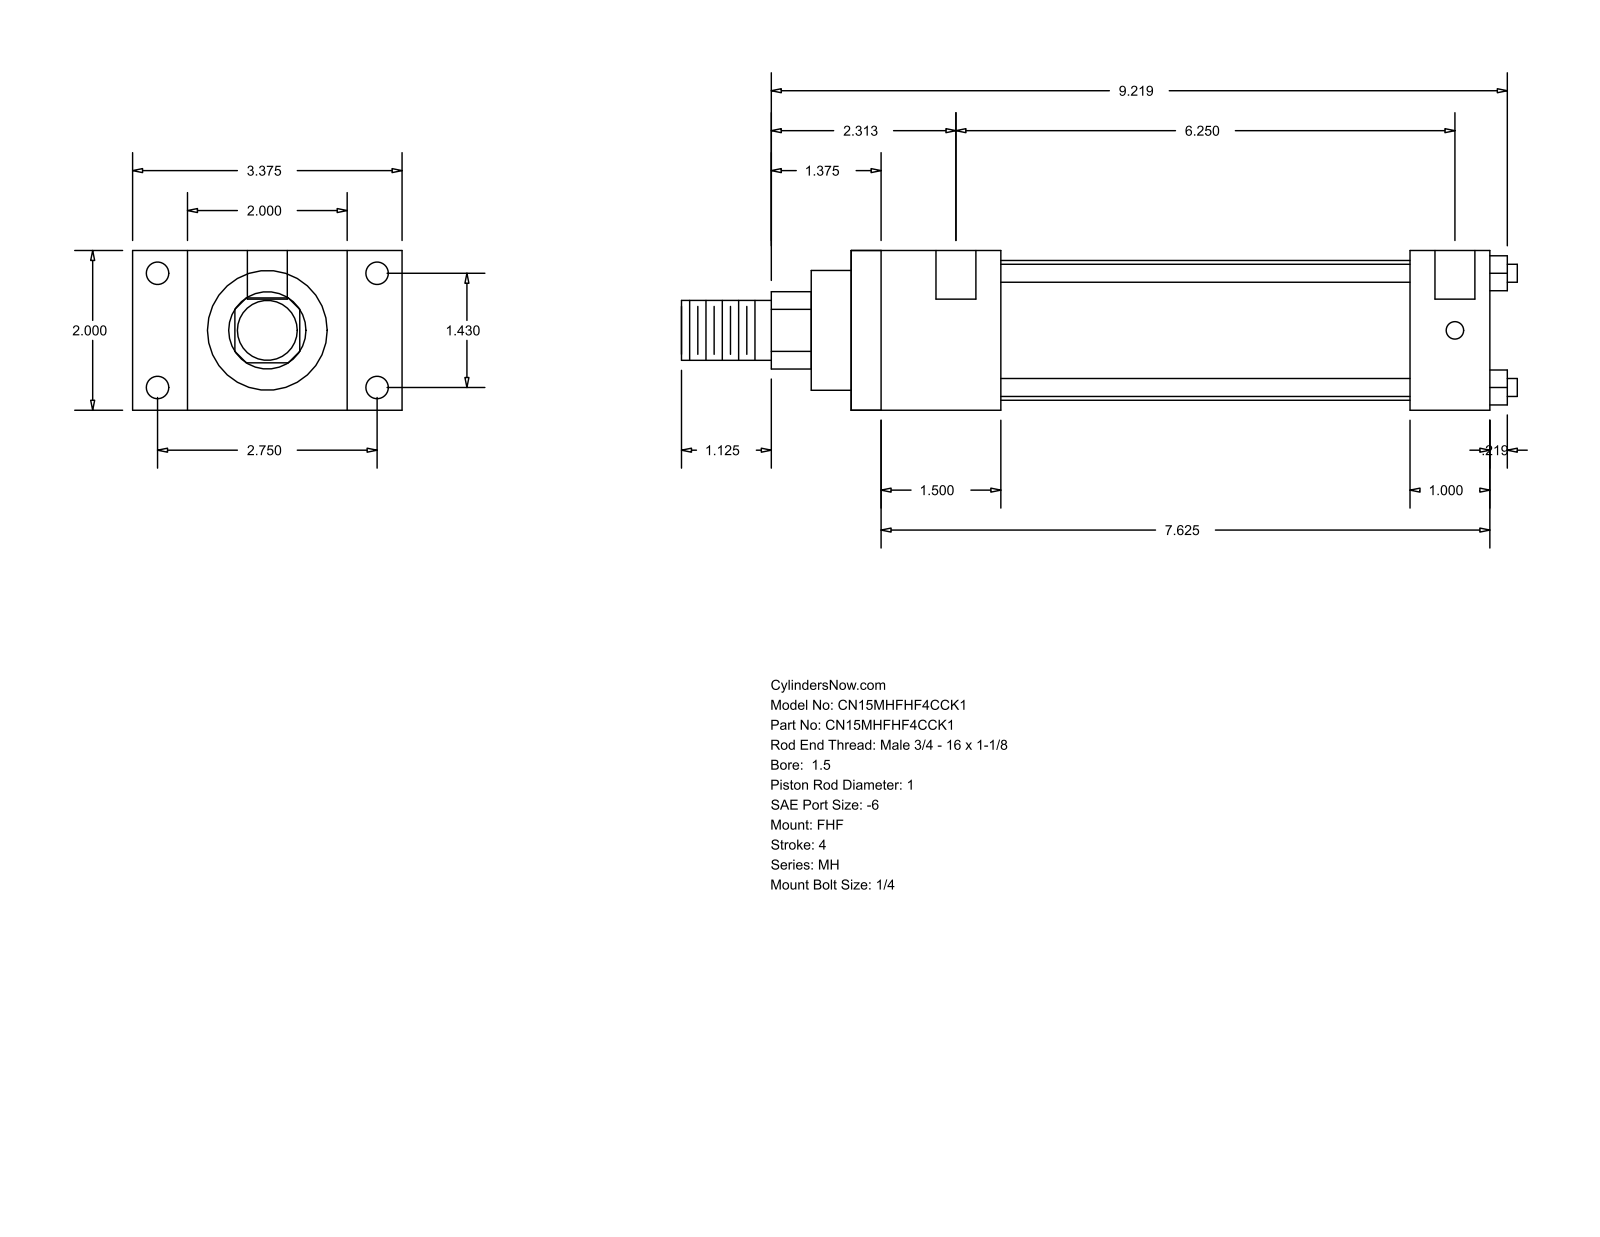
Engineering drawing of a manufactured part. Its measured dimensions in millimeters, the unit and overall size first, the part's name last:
Units: millimetres
Overall size (bounding box): 265.91 × 85.72 × 50.8
Round holes (diameter × count): ⌀5.56 ×4, ⌀7.14 ×4, ⌀12.7 ×2
Round bosses / shafts (diameter × count): ⌀5.71 ×4, ⌀44.45 ×1, ⌀38.1 ×1, ⌀25.4 ×1, ⌀19.05 ×1
Partial cylindrical surfaces — rounded edges, fillets, slot ends (radius × count): R12.29 ×1
Main face-to-face distances: 50.8, 17.46, 68.26, 47.63, 85.72, 203.2, 155.57, 25.4, 177.8, 130.17
Hole centre spacings: 36.32, 69.84, 78.72, 161.93, 3.18, 158.75
Bodies: 0 solids, 88 faces (60 planar, 28 cylindrical, 0 other)
Part name (STEP PRODUCT): MH_FHF__0150_1
STEP written by: GSSL Pune (CONFIG_CONTROL_DESIGN)
